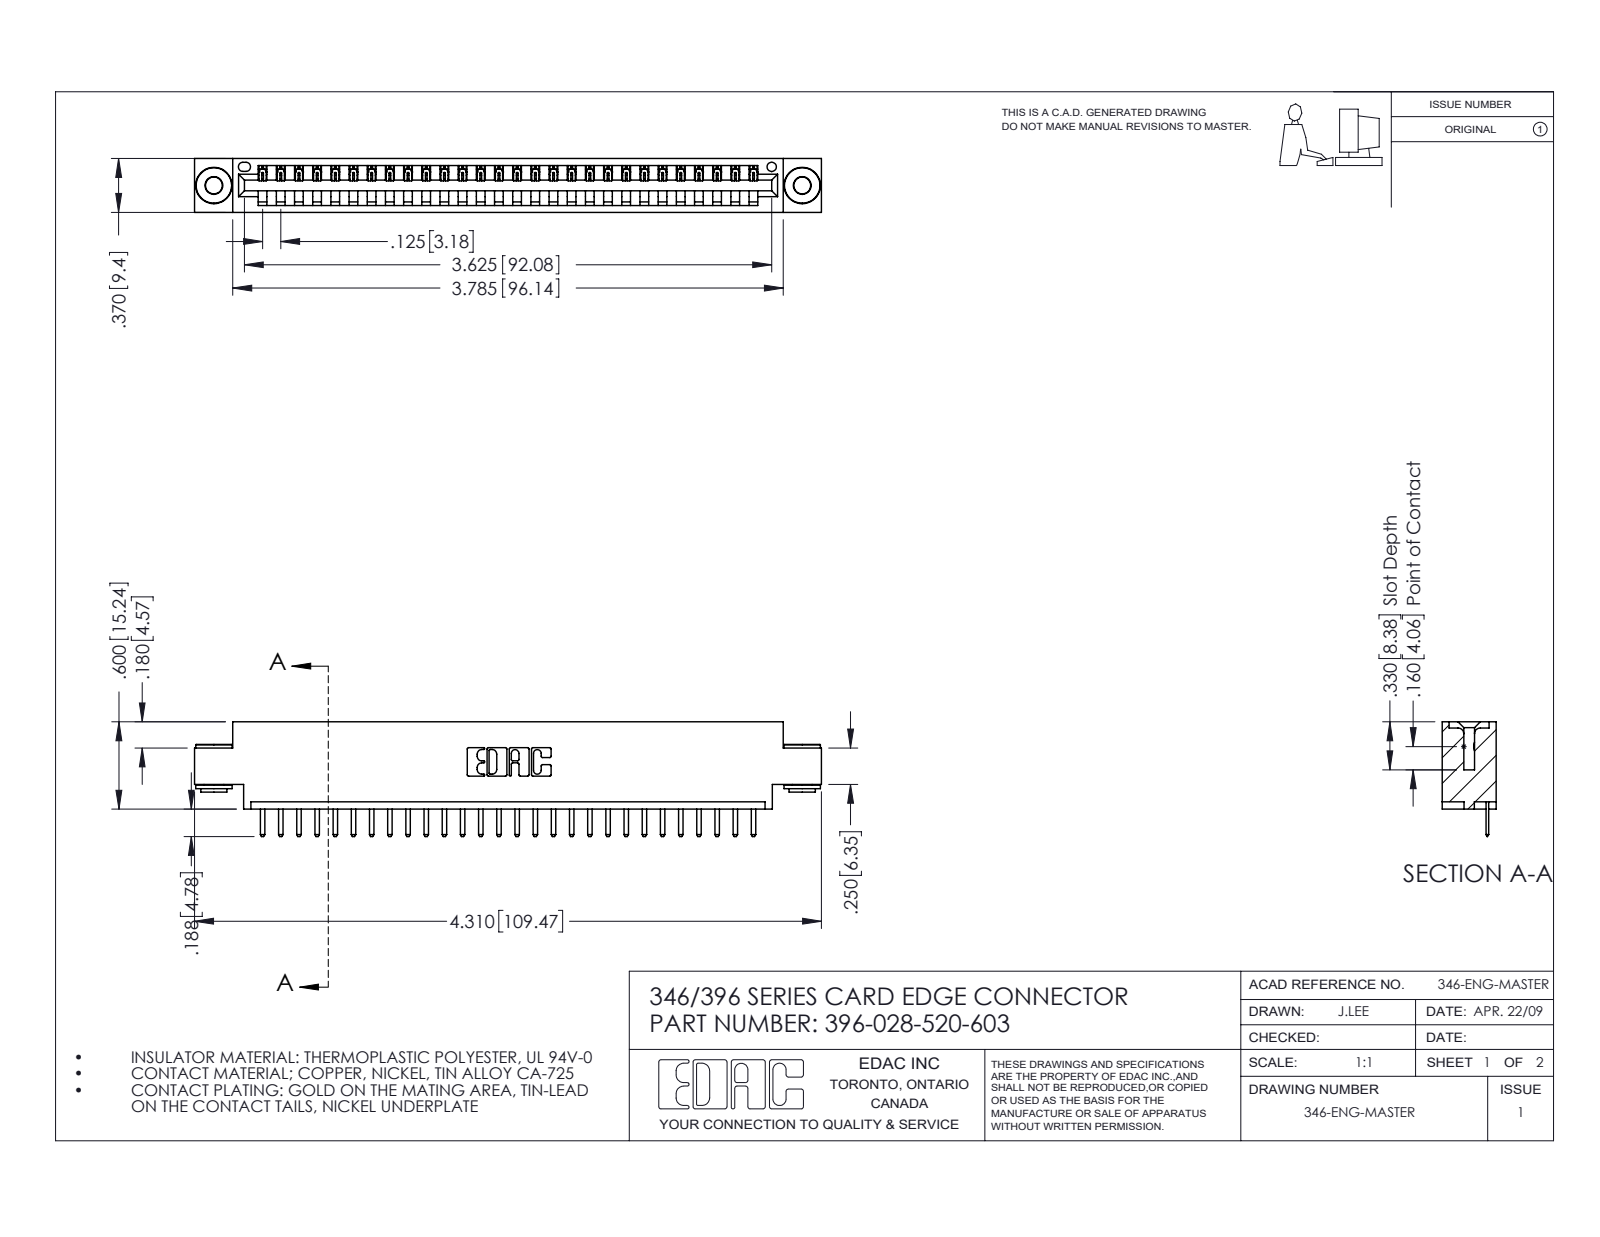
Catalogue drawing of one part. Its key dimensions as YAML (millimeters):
part_name: "345-250-002_345-250-002-102; 396-028-520-603; 346 Part_0.170 Offset - 0.156 Dia-TH; 345-292-001_345-293-120"
step_written_by: "SolidWorks 2016 (CONFIG_CONTROL_DESIGN)"
units: millimeters
bodies: {solids: 31, faces: 1900, planar: 1266, cylindrical: 626, other: 8}
overall_size: [109.5, 20, 9.4]
volume: 10200
surface_area: 12660
round_holes:
  - {diameter: 2.9, count: 2}
  - {diameter: 4, count: 2}
  - {diameter: 1.6, count: 1}
round_bosses_or_shafts:
  - {diameter: 6.4, count: 2}
  - {diameter: 4.6, count: 2}
  - {diameter: 3.5, count: 2}
partial_cylinders:
  - {radius: 0.3, count: 58}
  - {radius: 0.2, count: 56}
  - {radius: 0.3, count: 22}
  - {radius: 0.2, count: 6}
  - {radius: 0.8, count: 6}
  - {radius: 0.7, count: 3}
  - {radius: 0.8, count: 2}
  - {radius: 1, count: 2}
face_to_face_distances: [9.4, 1.2, 8.2, 6.4, 0.6, 3.8, 5.6, 2.5, 4.4, 1.8]
hole_center_spacings: [6.2, 97.5, 102.7]
